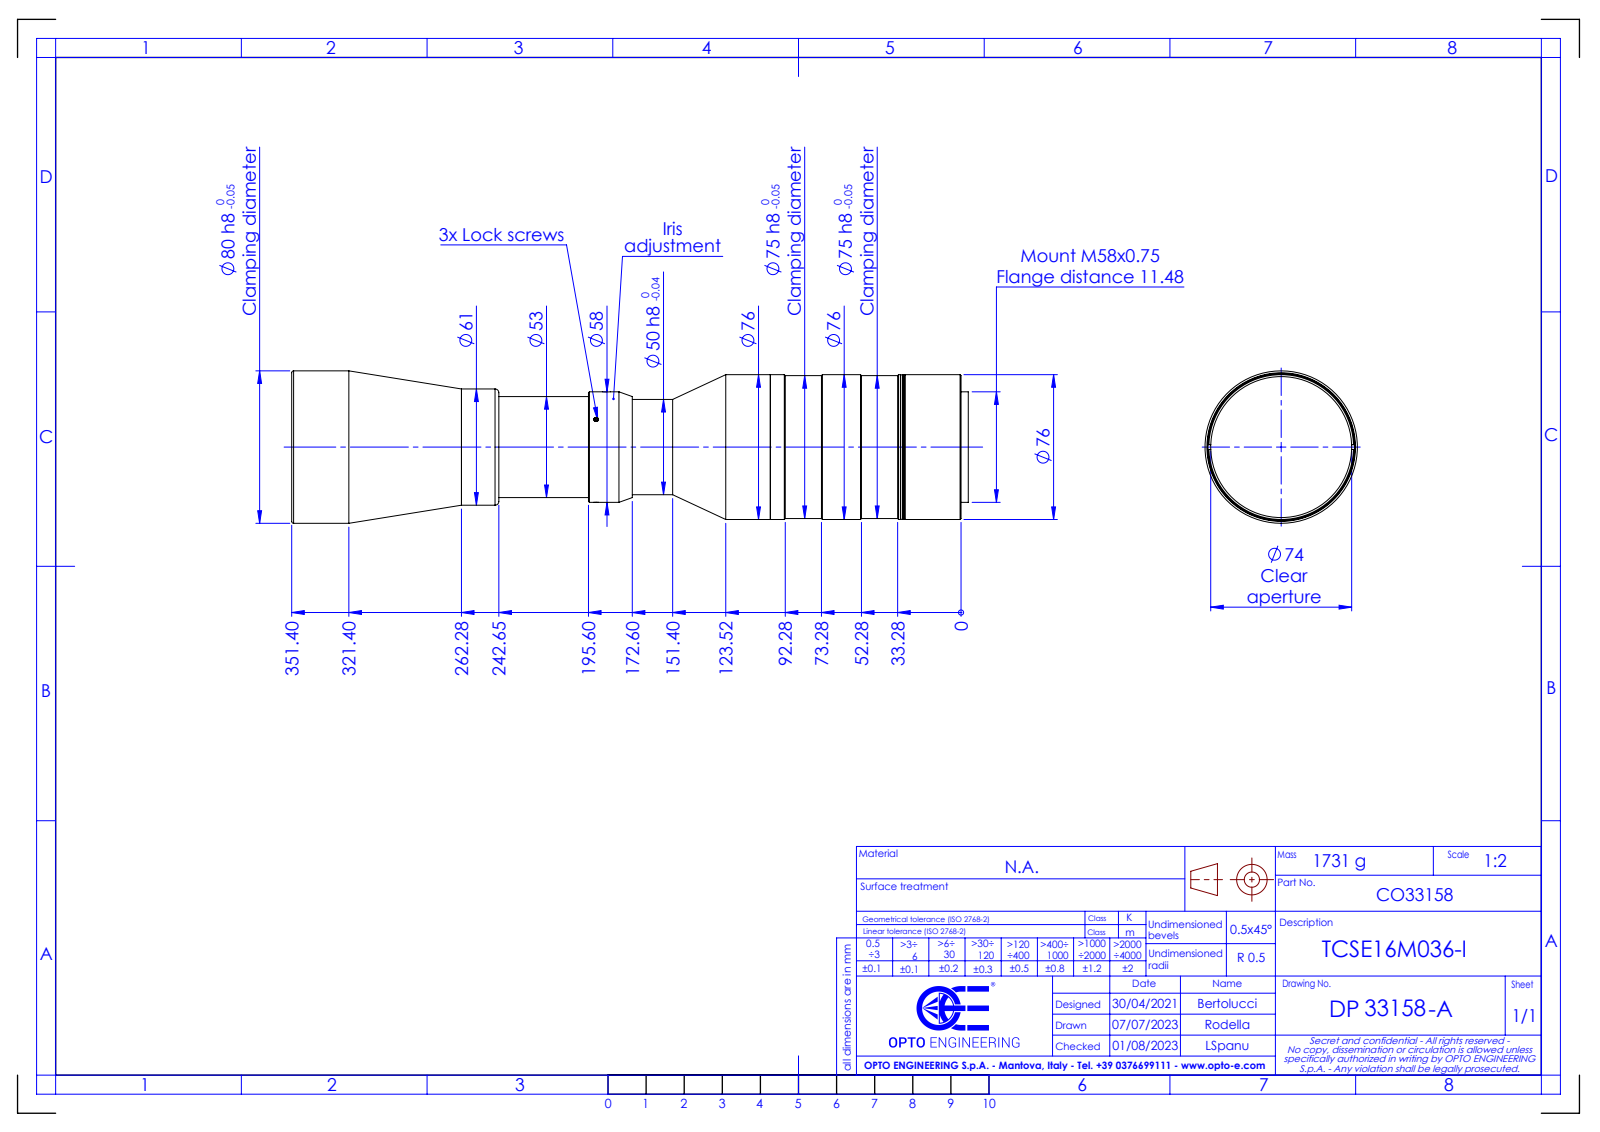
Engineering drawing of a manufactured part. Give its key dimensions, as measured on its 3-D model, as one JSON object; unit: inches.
{"part_name": "DP33158-A_TCSE16M036-I", "step_written_by": "SolidWorks 2021 (CONFIG_CONTROL_DESIGN)", "units": "inches", "bodies": {"solids": 0, "faces": 129, "planar": 43, "cylindrical": 46, "other": 40}, "overall_size": [13.984, 3.15, 3.15], "round_holes": [[0.165, 1], [2.126, 1], [2.52, 1], [2.717, 1], [2.913, 1], [3.031, 1]], "round_bosses_or_shafts": [[3.15, 1], [2.992, 1], [2.984, 1], [2.953, 1], [2.402, 1], [2.283, 1], [2.087, 1], [1.969, 1]], "face_to_face_distances": [7.701, 3.759, 3.942, 7.324, 3.565, 0.377, 2.625, 6.384, 9.949, 10.326]}
